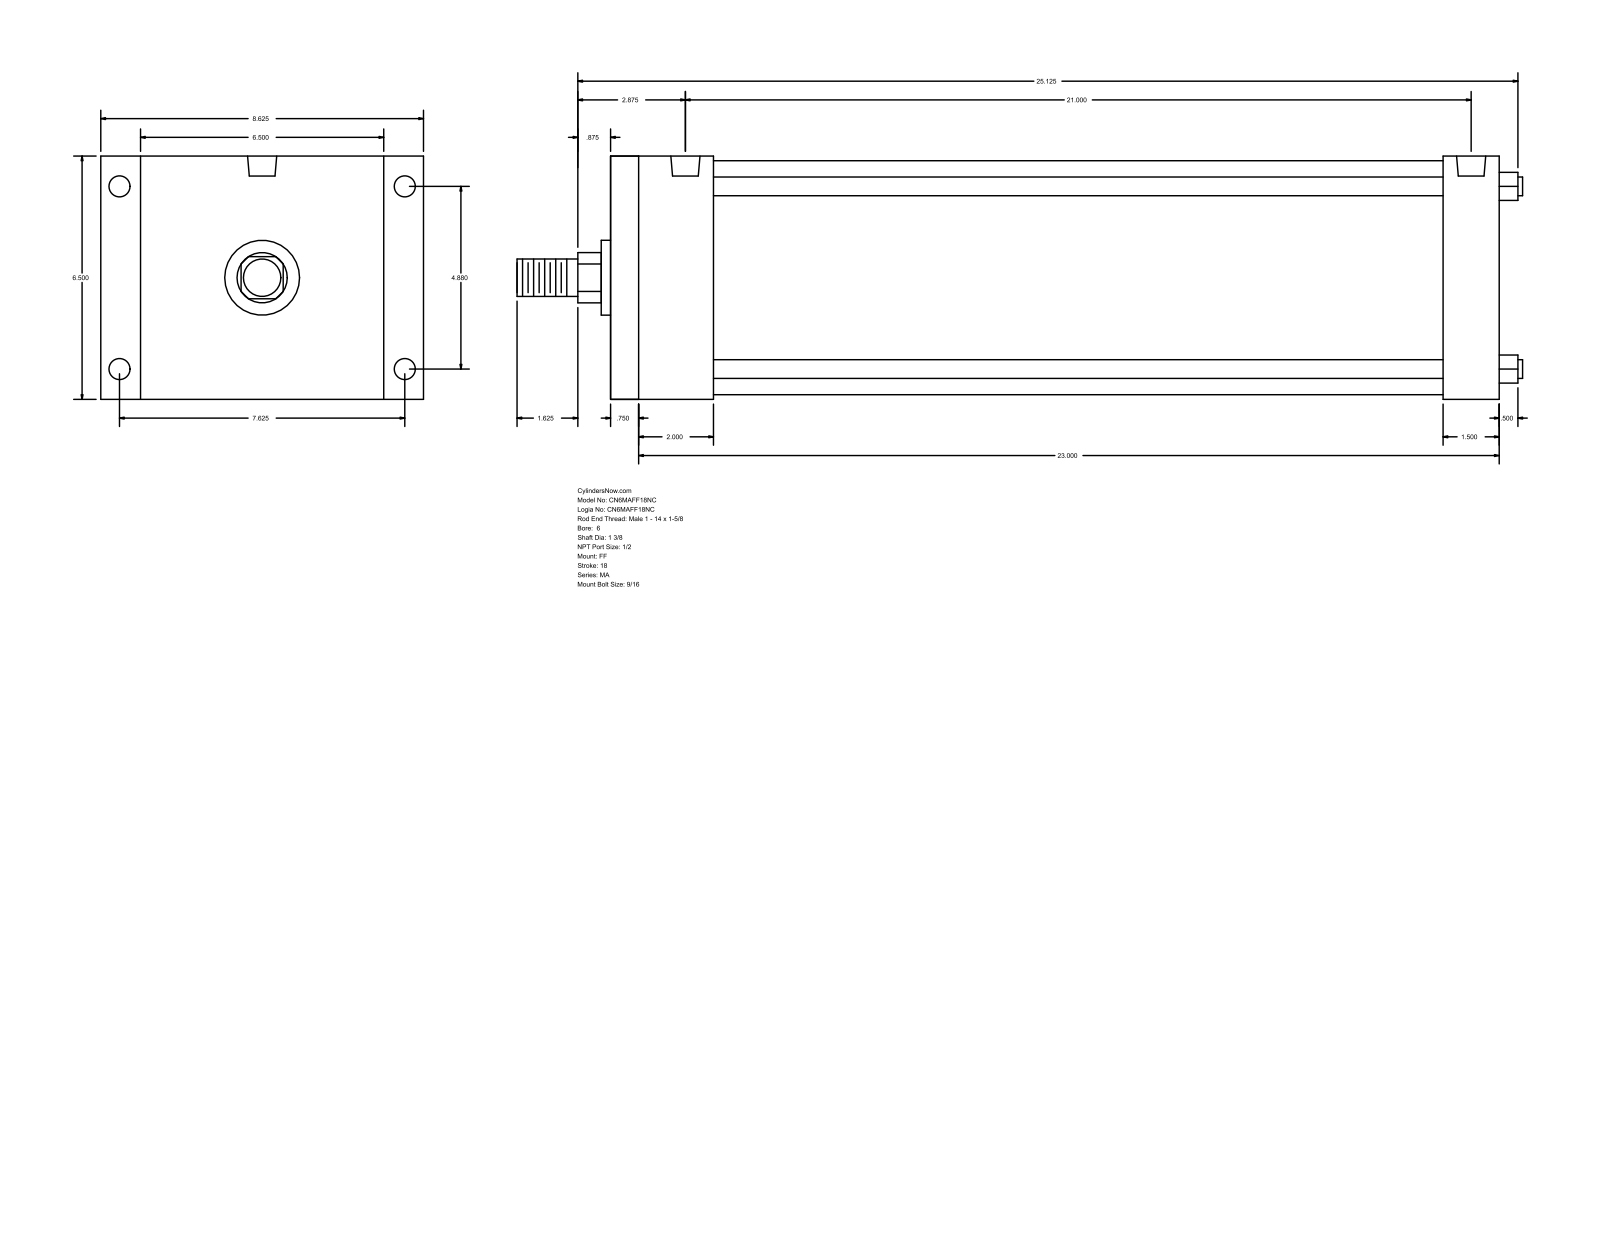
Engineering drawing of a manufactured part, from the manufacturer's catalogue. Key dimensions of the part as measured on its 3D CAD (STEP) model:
Part name (STEP PRODUCT): MA_FF__0600_1.375
STEP written by: GSSL Pune (CONFIG_CONTROL_DESIGN)
Units: millimetres
Bodies: 0 solids, 92 faces (64 planar, 28 cylindrical, 0 other)
Overall size (bounding box): 682.62 × 219.07 × 165.1
Round holes (diameter × count): ⌀14.29 ×4, ⌀17.46 ×4, ⌀19.77 ×2
Round bosses / shafts (diameter × count): ⌀12.7 ×4, ⌀158.75 ×1, ⌀50.8 ×1, ⌀34.92 ×1, ⌀25.4 ×1
Partial cylindrical surfaces — rounded edges, fillets, slot ends (radius × count): R17.06 ×1
Main face-to-face distances: 165.1, 603.25, 15.87, 587.38, 38.1, 66.67, 50.8, 536.58, 565.15, 549.28
Hole centre spacings: 123.96, 193.68, 229.95, 536.57, 3.18, 533.39
